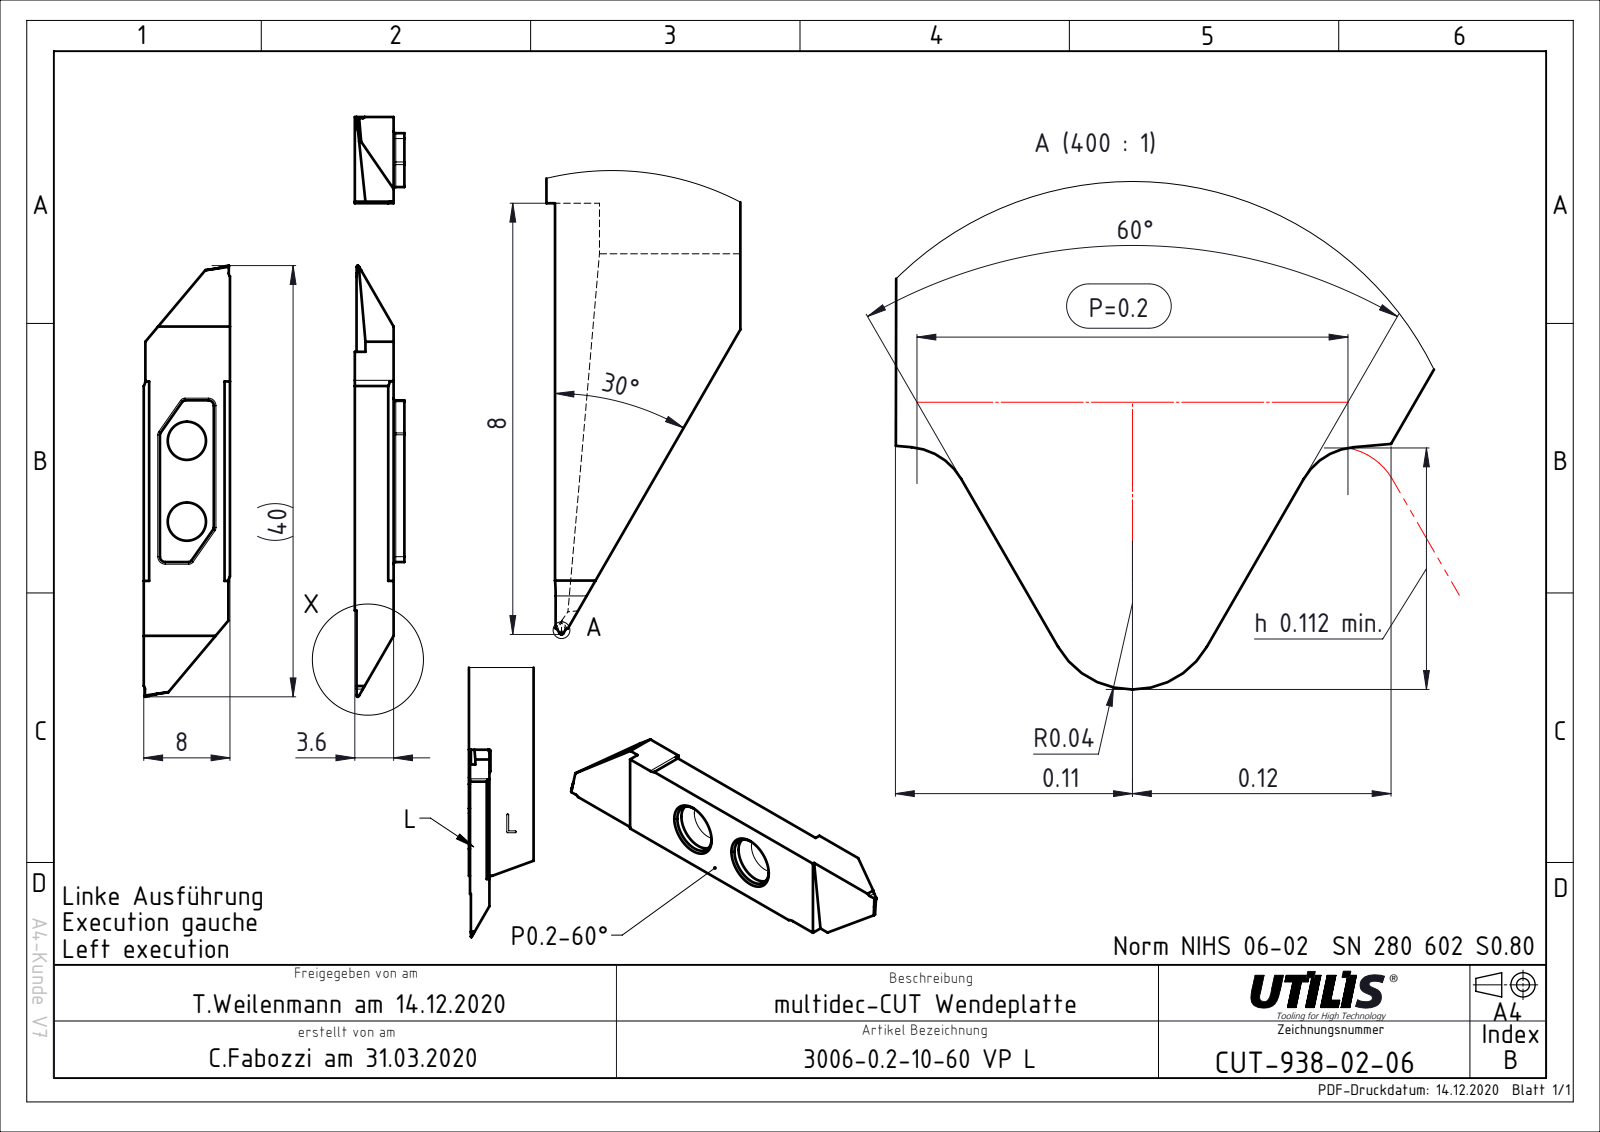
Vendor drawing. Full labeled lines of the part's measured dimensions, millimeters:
Part name (STEP PRODUCT): CUT-938-02; ASME Y14.5
STEP written by: FormatWorks Professional (AP242_MANAGED_MODEL_BASED_3D_ENGINEERING_MIM_LF)
Units: millimetres
Bodies: 1 solid, 46 faces (30 planar, 16 cylindrical, 0 other)
Overall size (bounding box): 40 × 8 × 3.6
Volume: 809 mm³ · Surface area: 841 mm²
Round holes (diameter × count): ⌀3.55 ×2
Partial cylindrical surfaces — rounded edges, fillets, slot ends (radius × count): R1 ×2
Main face-to-face distances: 3.6, 8, 7.85, 22.54, 7.7, 24, 4, 4.15, 11.85, 12
Hole centre spacings: 7.5
